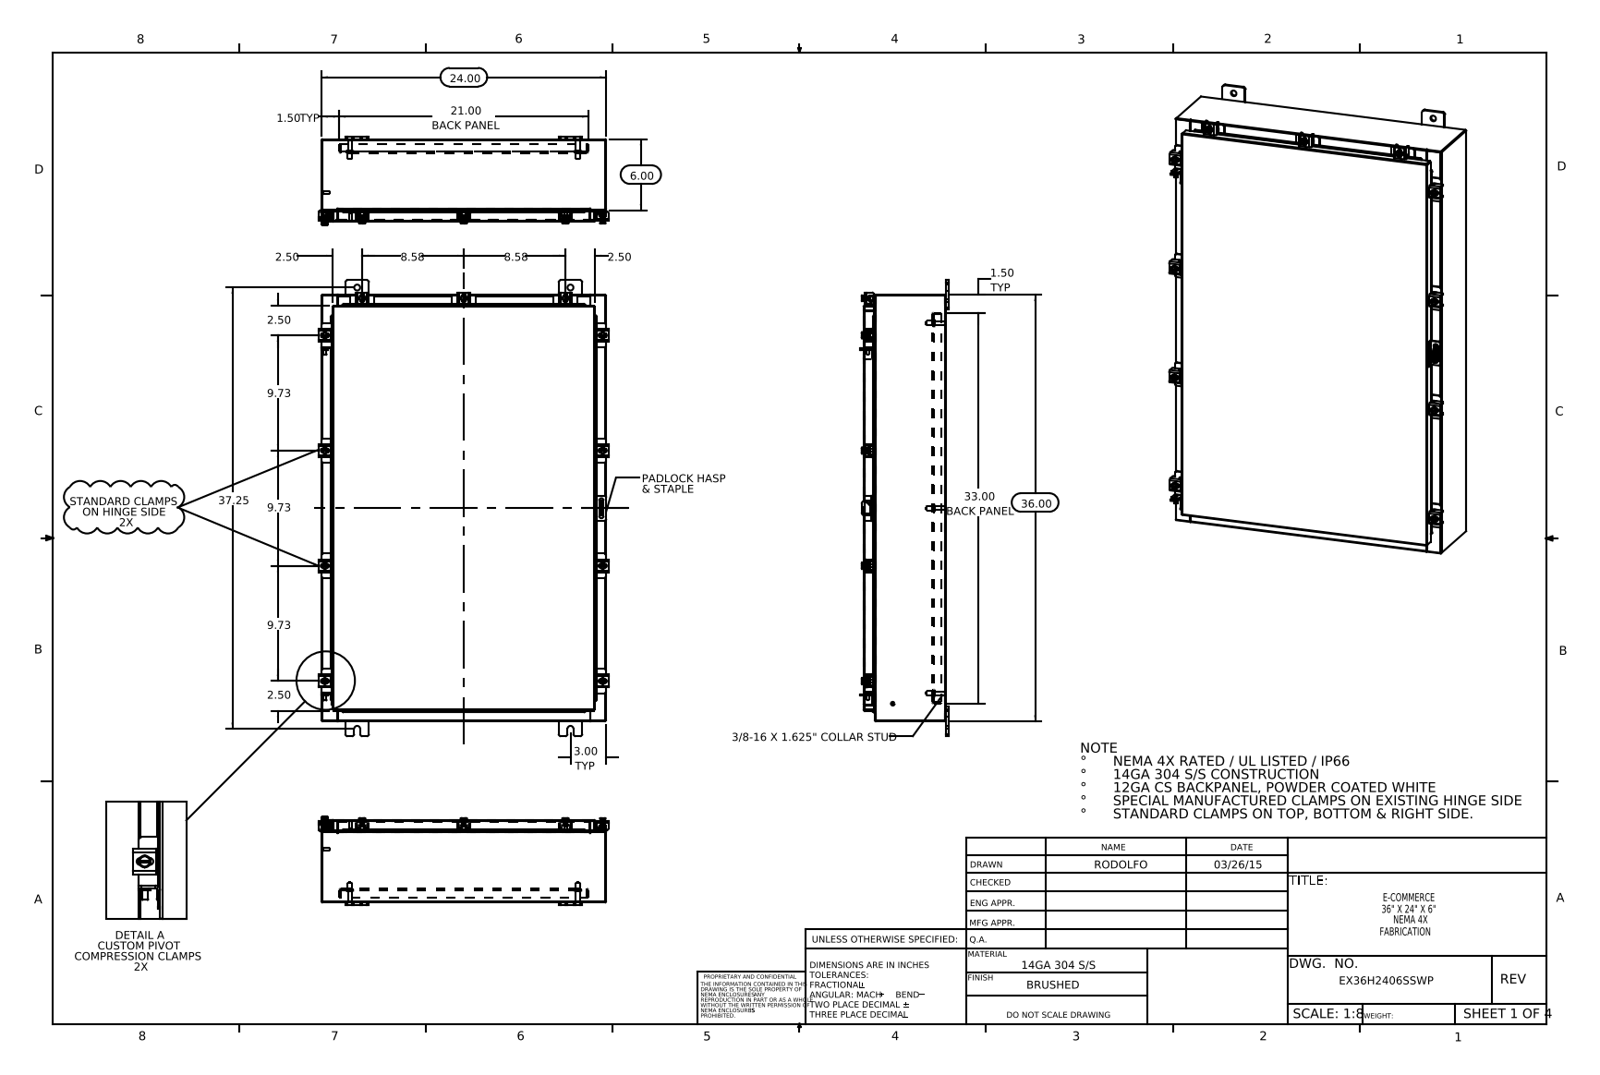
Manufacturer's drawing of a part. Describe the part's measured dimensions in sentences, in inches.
The part is named "N-WMT04X30402202210-00 Clamp Top; EX36H2406SSWP Padlock Staple; Clamp Top_RTP31; HW-CLN-NH-20330 (+8 more)". Its 3-D file was written by "SolidWorks 2014 (CONFIG_CONTROL_DESIGN)". It is 78 solids with 1971 faces: 1041 planar, 758 cylindrical and 172 other. Overall it measures 38.5 by 24.421 by 7.453 inches. Its volume is 290.3 cubic inches and its surface area 7 154 square inches. Round holes: 11 of diameter 0.213, 11 of diameter 0.26, 10 of diameter 0.5, 1 of diameter 0.125, 1 of diameter 0.25. Round bosses or shafts: 11 of diameter 0.5, 11 of diameter 0.25, 9 of diameter 0.399, 6 of diameter 0.625, 6 of diameter 0.375, 6 of diameter 0.33, 2 of diameter 0.315, 2 of diameter 0.236. Partial cylindrical surfaces (rounded edges, fillets, slot ends): 48 of radius 0.06, 26 of radius 0.013, 24 of radius 0.19, 22 of radius 0.088, 22 of radius 0.141, 20 of radius 0.09, 20 of radius 0.12, 19 of radius 0.05. The main face-to-face distances are 0.075, 6.9, 6.975, 6.826, 0.104, 1, 1.075, 5.826, 5.9, 1.179. The hole center spacings are 25.389, 5.299, 9.73, 10.964, 14.744, 15.625, 19.459, 20.597.
